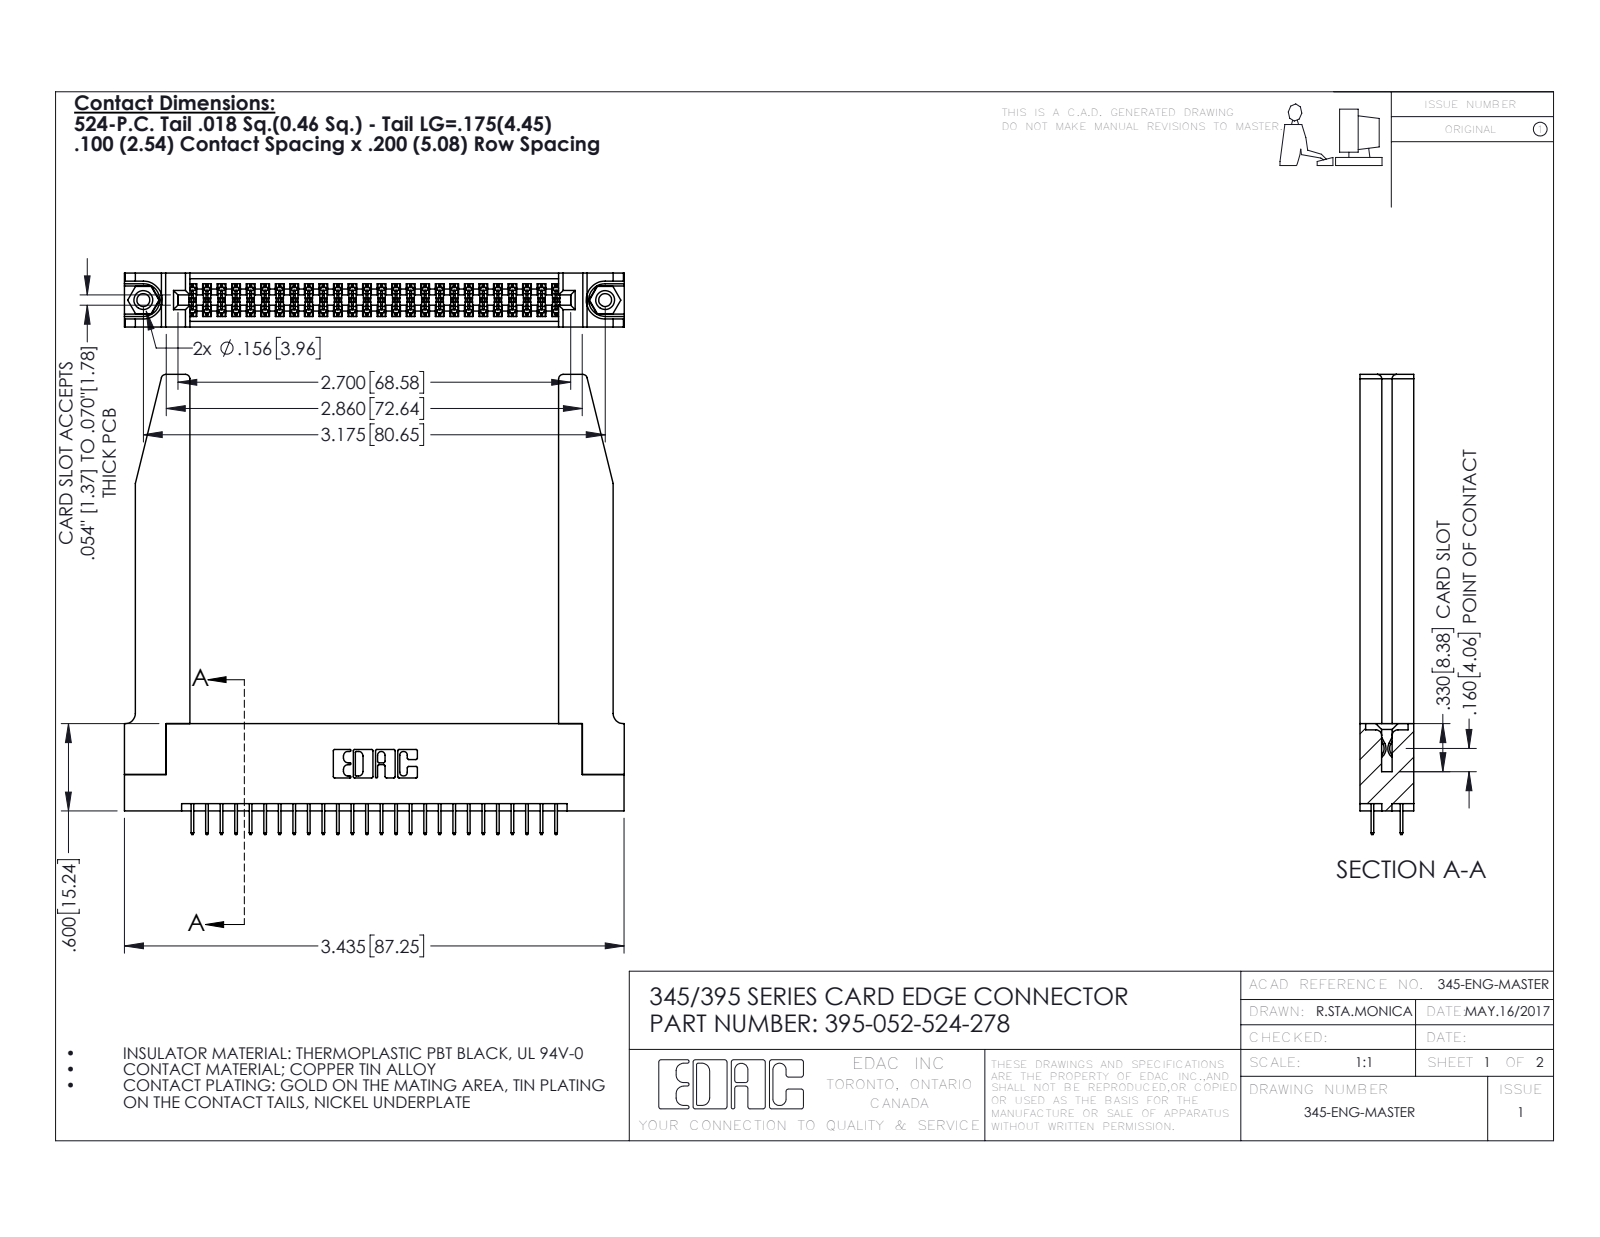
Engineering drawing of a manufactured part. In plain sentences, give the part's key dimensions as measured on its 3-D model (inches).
The part is named "345 Part_Flush Mounting Lugs - 0.156 Dia-TH; 395-052-524-278; 345-220-078_345-220-078; 345-250-001_345-250-001-102 (+1 more)". Its 3-D file was written by "SolidWorks 2016 (CONFIG_CONTROL_DESIGN)". It is 57 solids with 3168 faces: 2250 planar, 866 cylindrical and 52 other. Overall it measures 3.436 by 3.162 by 0.37 inches. Its volume is 0.978 cubic inches and its surface area 28.7 square inches. Round holes: 2 of diameter 0.089, 2 of diameter 0.125, 2 of diameter 0.156, 1 of diameter 0.064. Round bosses or shafts: 2 of diameter 0.155. Partial cylindrical surfaces (rounded edges, fillets, slot ends): 78 of radius 0.006, 22 of radius 0.01, 8 of radius 0.03, 6 of radius 0.007, 6 of radius 0.031, 3 of radius 0.026, 2 of radius 0.014, 2 of radius 0.019. The main face-to-face distances are 0.37, 0.072, 0.298, 0.2, 0.098, 0.272, 0.025, 0.225, 0.148, 0.15. The hole center spacings are 0.27, 2.94, 3.175.
